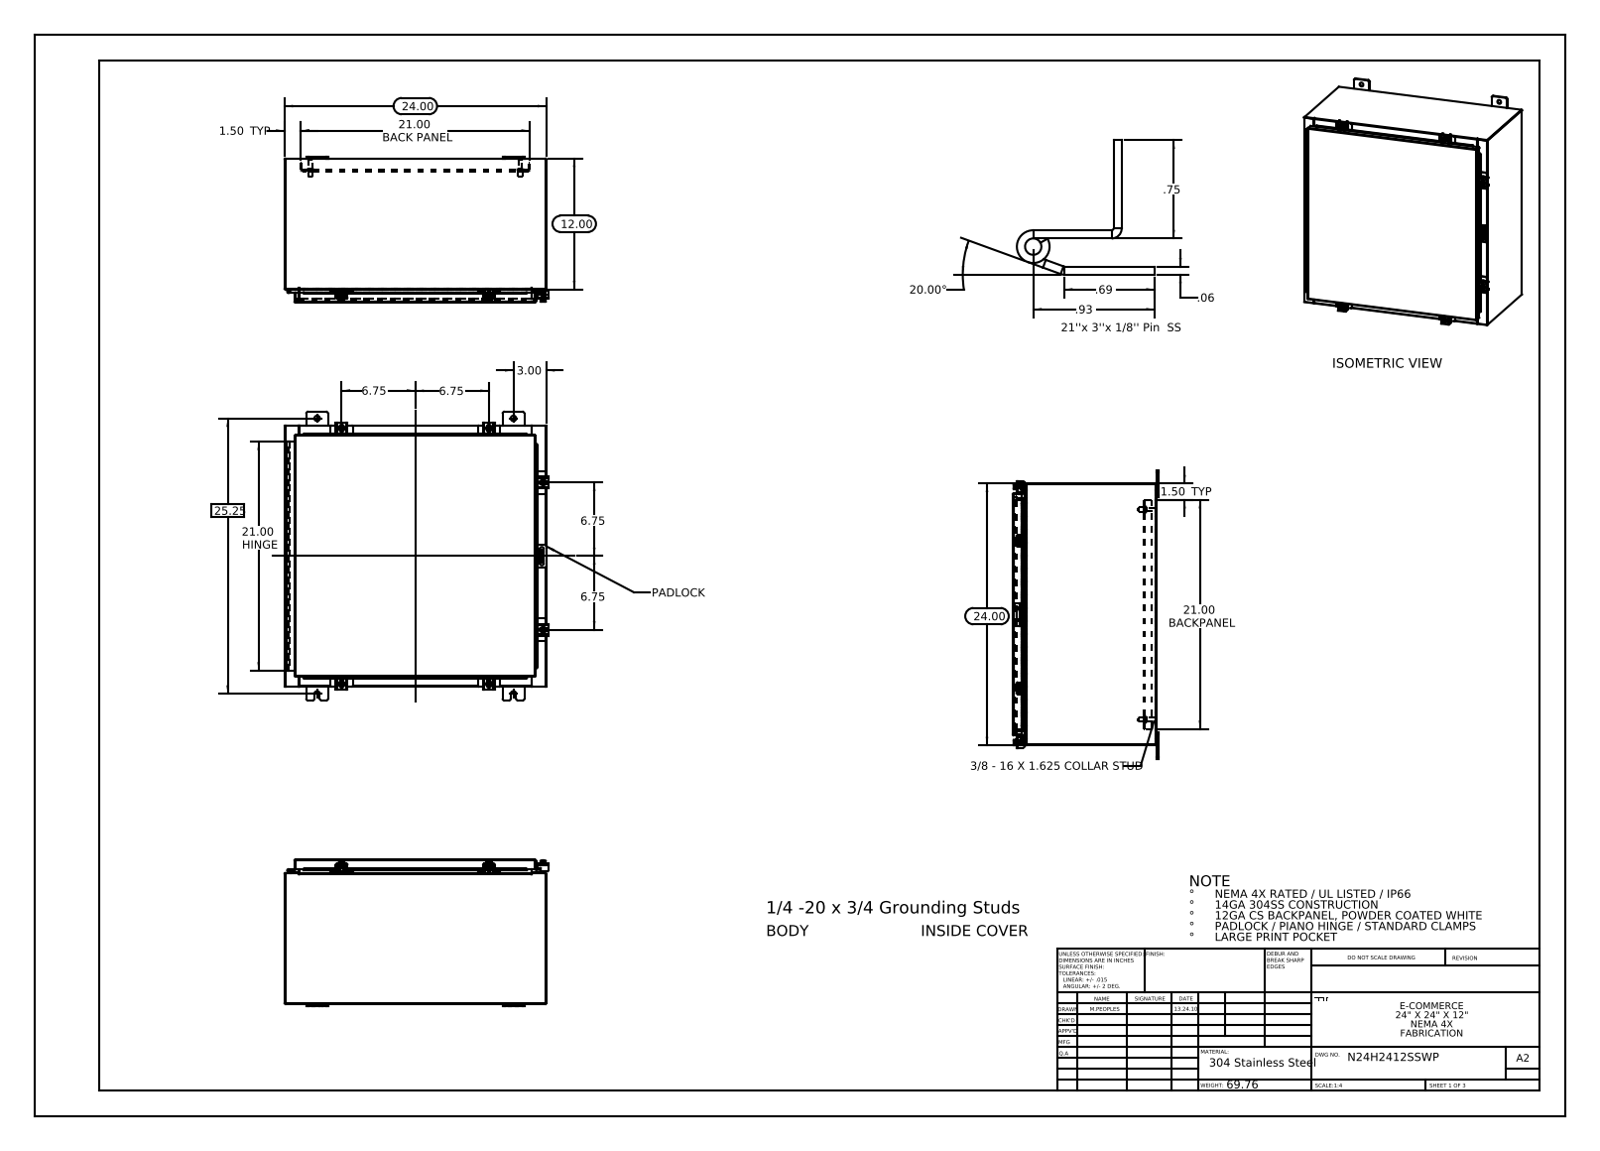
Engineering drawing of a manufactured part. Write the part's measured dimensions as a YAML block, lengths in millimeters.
part_name: "N24H2412SSWP Clamp Assembly; N24H2412SSWP 125 Pin Hinge; N24H2412SSWP Hinge Enclosure Side2; N24H2412SSWP Mounting Feet (+8 more)"
step_written_by: "SolidWorks 2013 (CONFIG_CONTROL_DESIGN)"
units: millimeters
bodies: {solids: 47, faces: 1709, planar: 908, cylindrical: 705, other: 96}
overall_size: [673.1, 615, 340.1]
volume: 4010000
surface_area: 3997000
round_holes:
  - {diameter: 12.7, count: 8}
  - {diameter: 5.4, count: 6}
  - {diameter: 6.6, count: 6}
  - {diameter: 3.2, count: 2}
  - {diameter: 3.2, count: 1}
round_bosses_or_shafts:
  - {diameter: 6.4, count: 7}
  - {diameter: 12.7, count: 6}
  - {diameter: 10.1, count: 6}
  - {diameter: 15.9, count: 4}
  - {diameter: 9.5, count: 4}
  - {diameter: 8.4, count: 4}
partial_cylinders:
  - {radius: 1.5, count: 30}
  - {radius: 0.3, count: 25}
  - {radius: 4.8, count: 24}
  - {radius: 2.2, count: 21}
  - {radius: 3, count: 12}
  - {radius: 3.6, count: 12}
  - {radius: 3.2, count: 10}
  - {radius: 1.3, count: 9}
face_to_face_distances: [1.9, 607.7, 333.4, 605.8, 609.6, 335.3, 331.5, 2.6, 25.4, 27.3]
hole_center_spacings: [419.3, 486, 547.2, 683.4, 342.9, 47.2, 57.8, 61.5]
